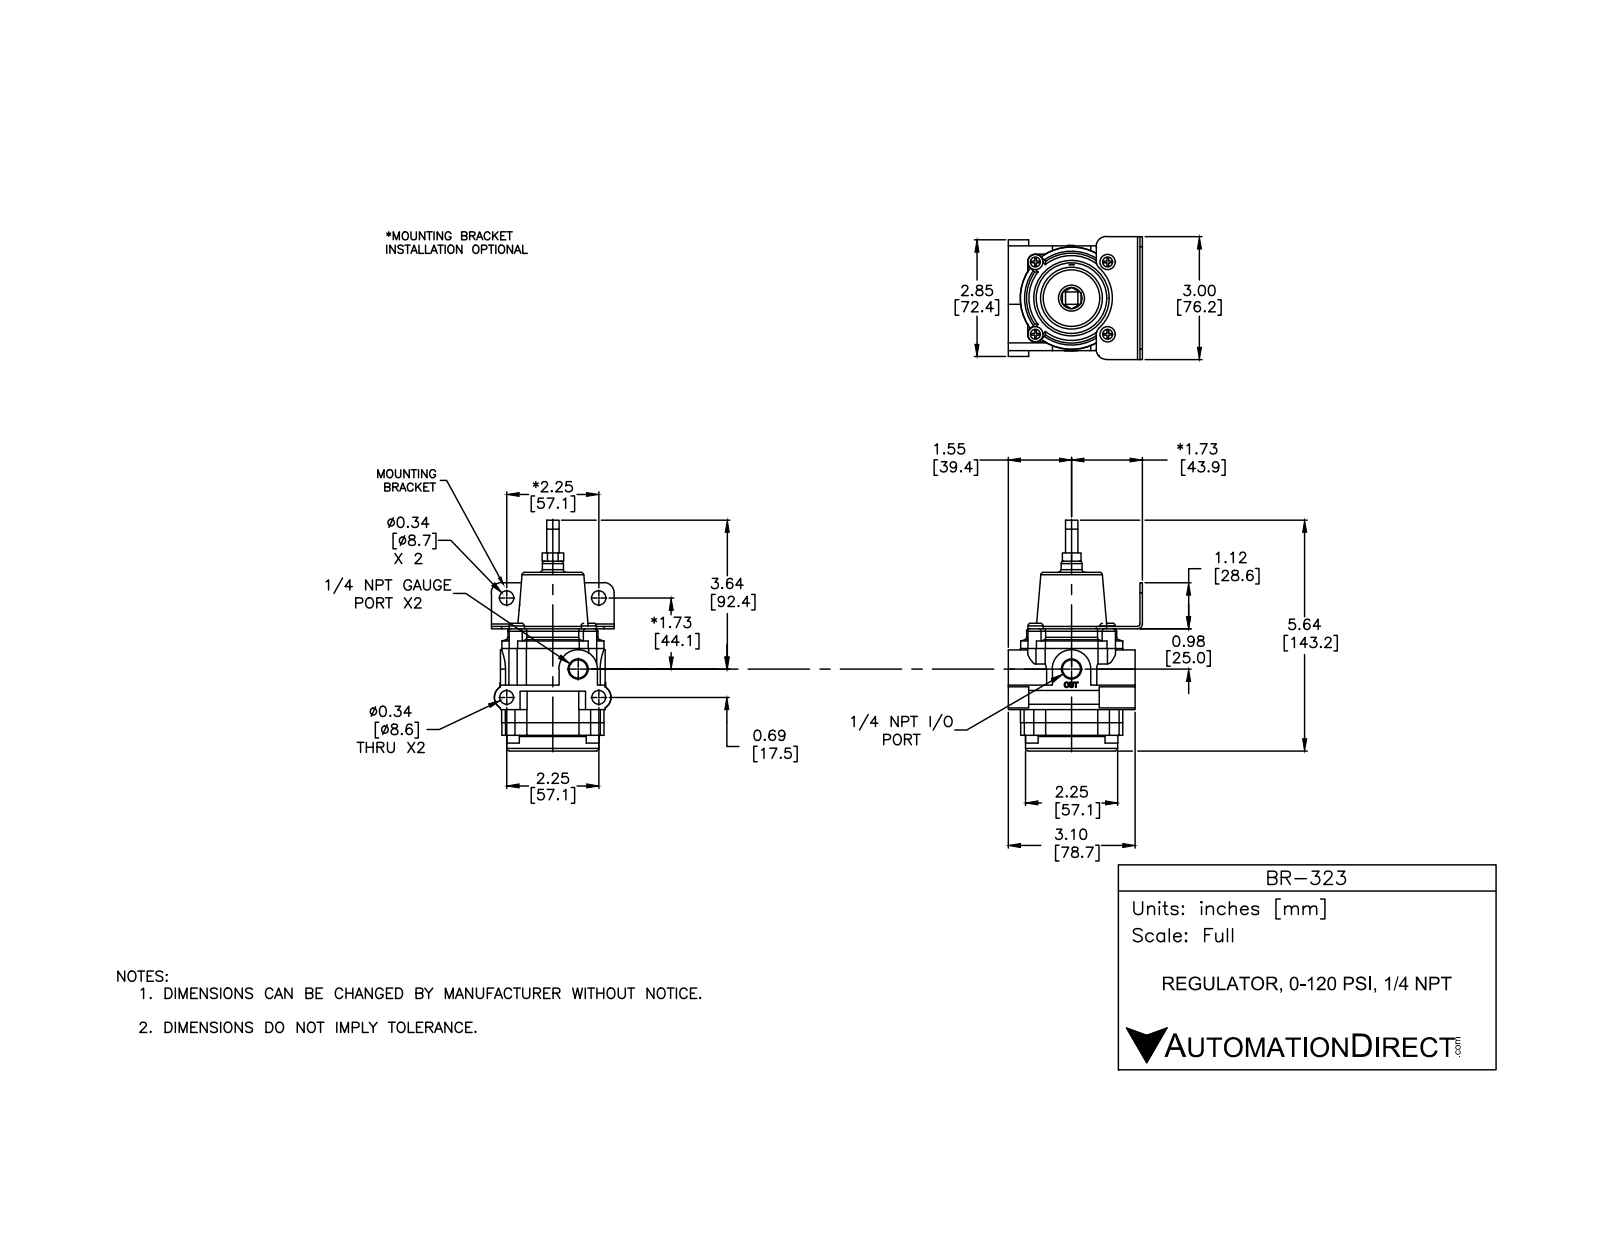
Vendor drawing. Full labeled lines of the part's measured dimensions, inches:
Part name (STEP PRODUCT): BR-323
STEP written by: SolidWorks 2015 (CONFIG_CONTROL_DESIGN)
Units: inches
Bodies: 13 solids, 1460 faces (268 planar, 963 cylindrical, 229 other)
Overall size (bounding box): 5.613 × 3.1 × 2.85
Volume: 18.6 in³ · Surface area: 96.84 in²
Round holes (diameter × count): ⌀0.159 ×8, ⌀0.201 ×8, ⌀0.34 ×2, ⌀0.438 ×2, ⌀0.257 ×1
Round bosses / shafts (diameter × count): ⌀0.19 ×8, ⌀0.149 ×8, ⌀0.312 ×5, ⌀0.373 ×4, ⌀2.2 ×1, ⌀0.512 ×1, ⌀0.203 ×1
Partial cylindrical surfaces — rounded edges, fillets, slot ends (radius × count): R0.004 ×48, R0.187 ×8, R0.188 ×8, R0.02 ×6, R0.062 ×4, R0.063 ×3, R0.3 ×2, R0.469 ×2
Main face-to-face distances: 1.81, 0.695, 2.505, 1.61, 0.915, 0.895, 0.385, 0.31, 1.225, 2.12
Hole centre spacings: 1.858, 0.125, 1.944, 1.375, 1.25, 1.25, 1.768, 1.768
